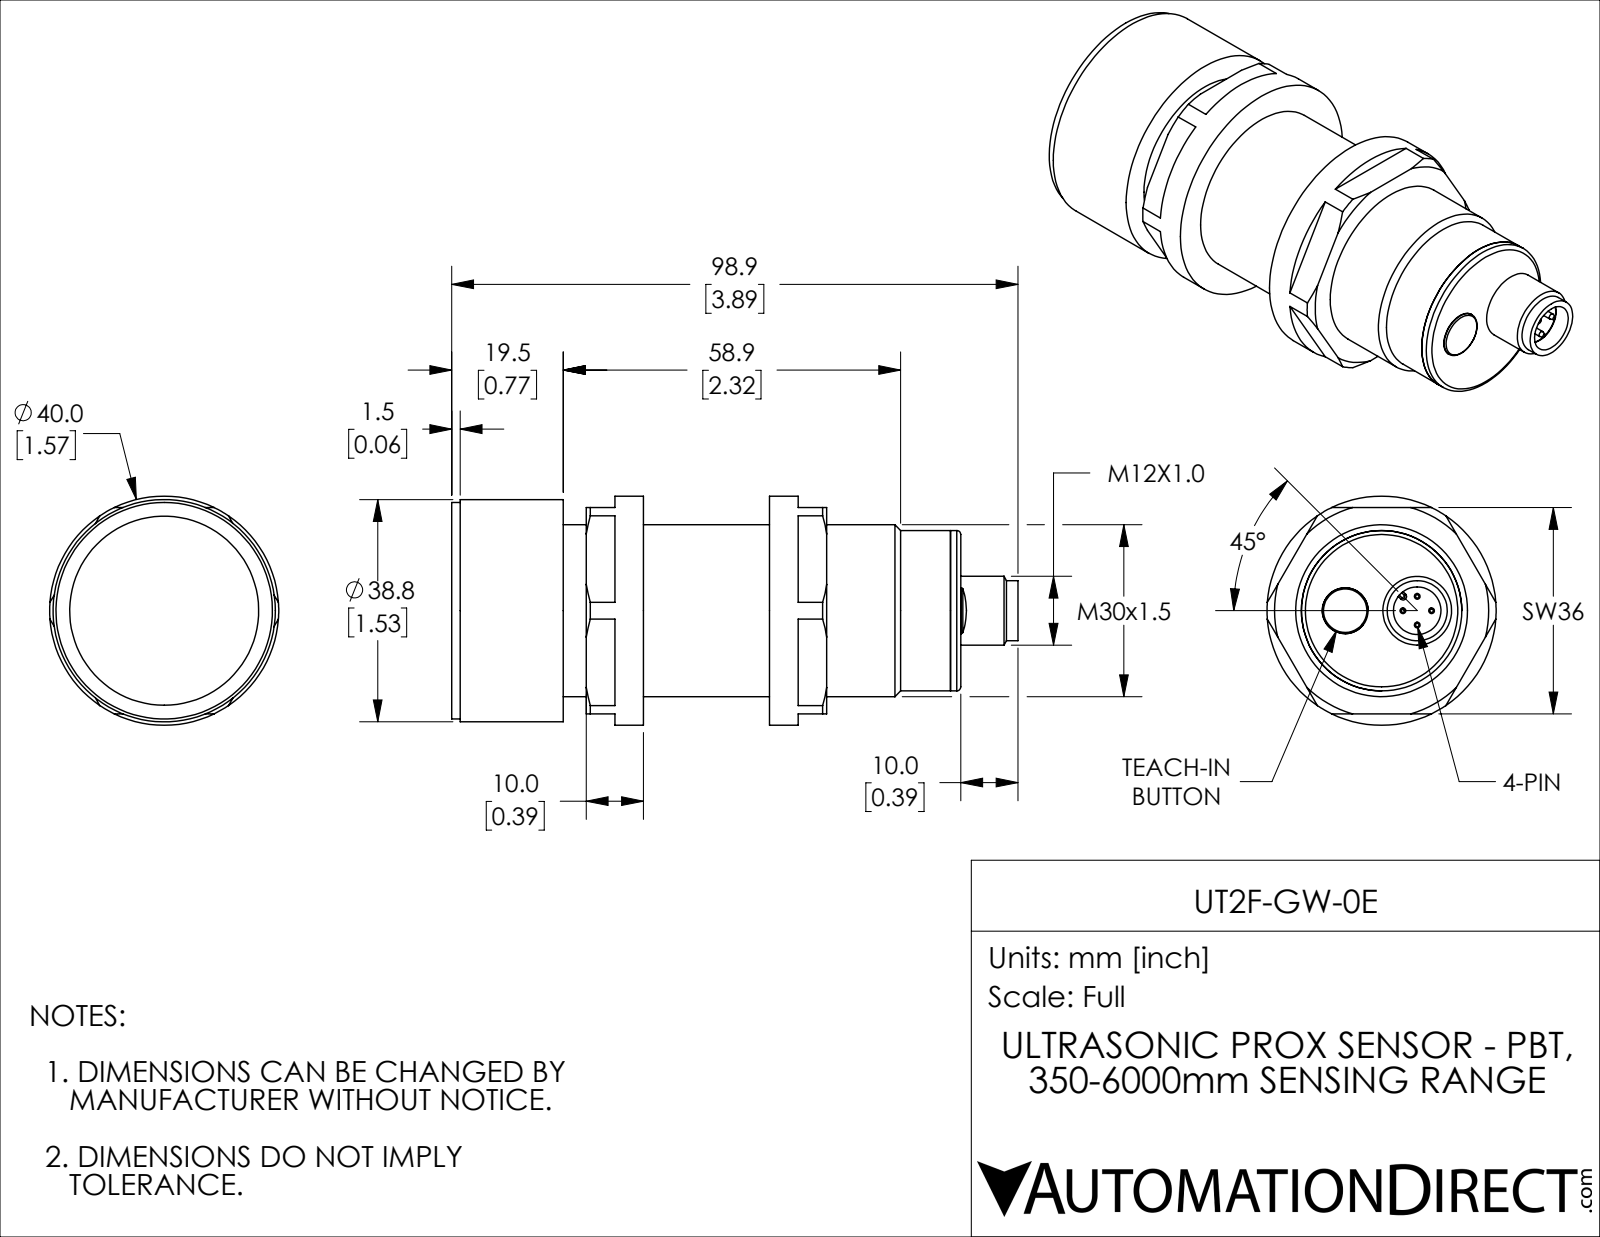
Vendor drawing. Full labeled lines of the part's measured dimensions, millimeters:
Part name (STEP PRODUCT): UT2F-GW-0E
STEP written by: SolidWorks 2018 (AUTOMOTIVE_DESIGN)
Units: millimetres
Bodies: 7 solids, 159 faces (59 planar, 55 cylindrical, 45 other)
Overall size (bounding box): 98.9 × 40 × 40
Volume: 81 199 mm³ · Surface area: 22 572 mm²
Round holes (diameter × count): ⌀1.8 ×4, ⌀8 ×1, ⌀8.3 ×1, ⌀9.45 ×1, ⌀30 ×1, ⌀33 ×1
Round bosses / shafts (diameter × count): ⌀1 ×4, ⌀40 ×1, ⌀38.8 ×1, ⌀37.8 ×1, ⌀28 ×1, ⌀12 ×1, ⌀10.5 ×1, ⌀9.25 ×1
Partial cylindrical surfaces — rounded edges, fillets, slot ends (radius × count): R0.3 ×2, R0.6 ×1
Main face-to-face distances: 32, 85.6, 36, 22, 1.49, 87.09, 10, 5, 31.6, 55.49
Hole centre spacings: 2.5, 3.54, 5, 6.7, 12.83, 3.72, 6.22, 6.36
